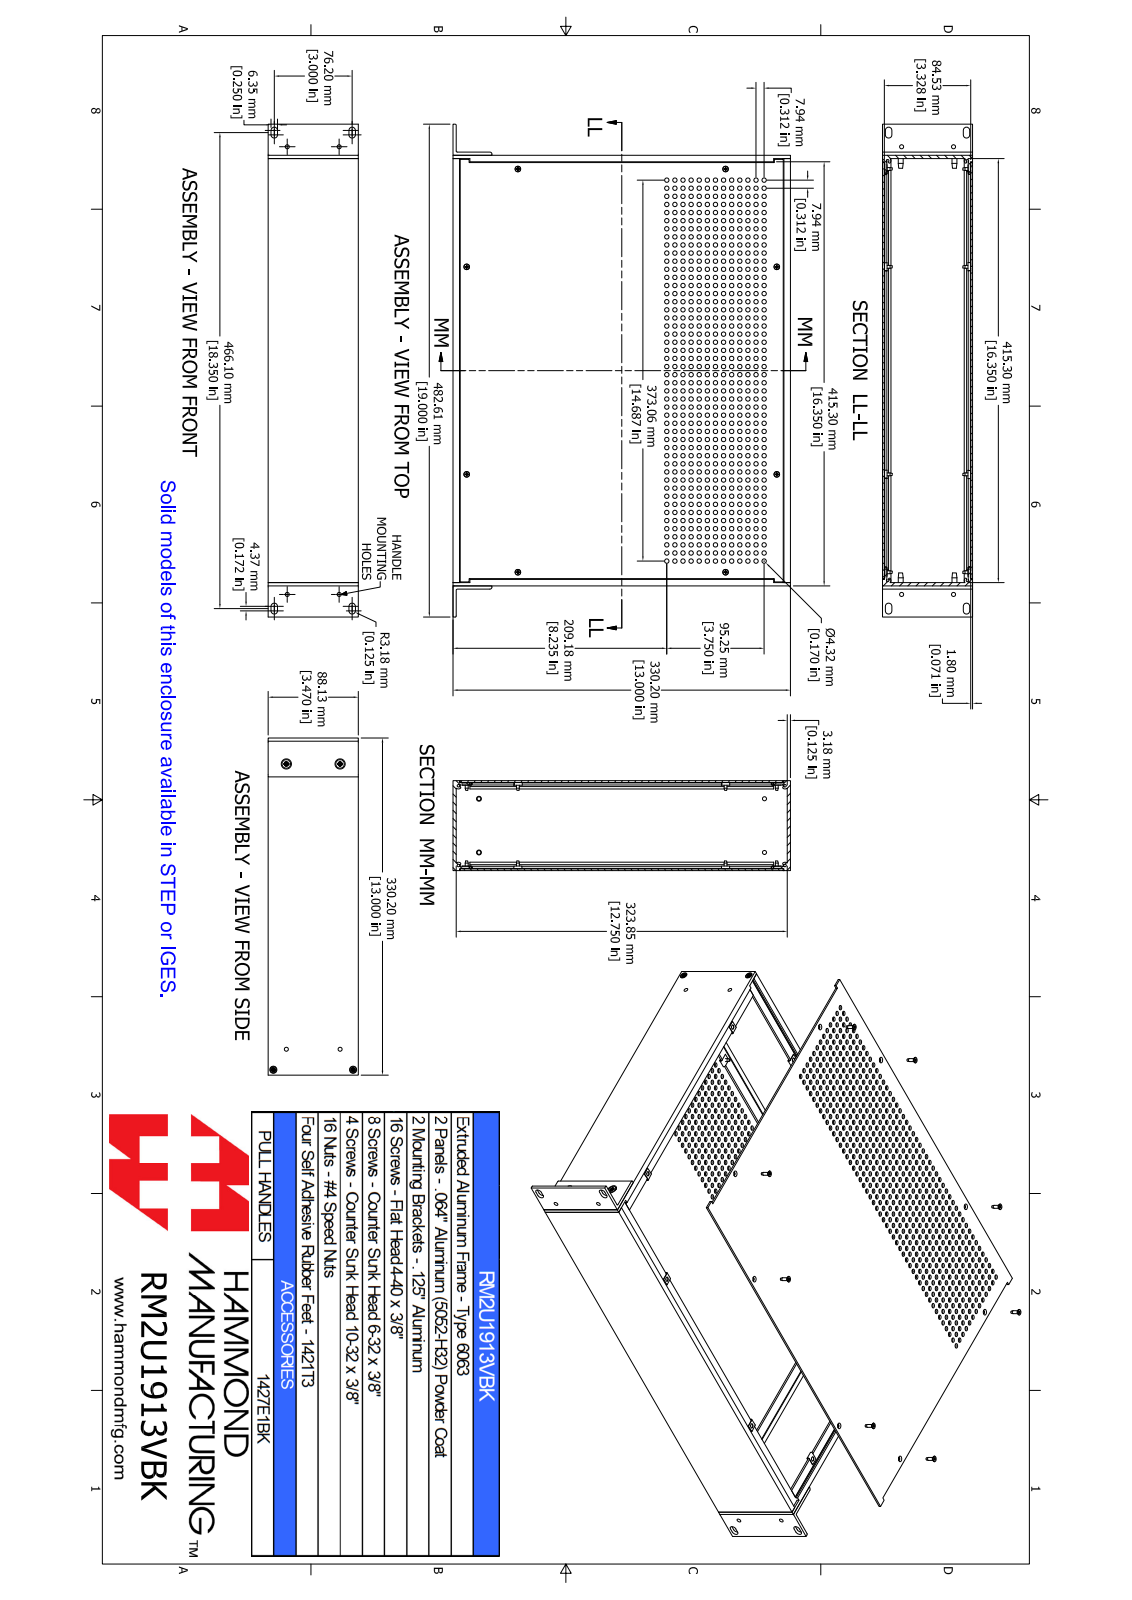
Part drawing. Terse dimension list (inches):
name: RM2U1913VBK
written by: SolidWorks 2021 (AUTOMOTIVE_DESIGN)
unit: in
bodies: 52 solids, 2600 faces (636 planar, 1468 cylindrical, 496 other)
size: 19 × 13 × 3.47
volume: 61.7 in³; area: 1 428 in²
holes: 624× ⌀0.17, 8× ⌀0.098, 8× ⌀0.118, 8× ⌀0.157, 8× ⌀0.169, 4× ⌀0.138, 4× ⌀0.156, 4× ⌀0.157, 2× ⌀0.197
bosses: 8× ⌀0.214, 8× ⌀0.112, 4× ⌀0.238, 4× ⌀0.138, 2× ⌀0.333, 2× ⌀0.19
rounds: 20× R0.039, 16× R0.125, 14× R0.049, 8× R0.05, 6× R0.037, 4× R0.038, 2× R0.079
face distances: 0.071, 3.399, 3.47, 3.328, 0.125, 0.125, 16.6, 13, 12.75, 12.875
hole spacings: 1.25, 0.313, 0.937, 2.5, 1.563, 2.187, 0.625, 0.625
